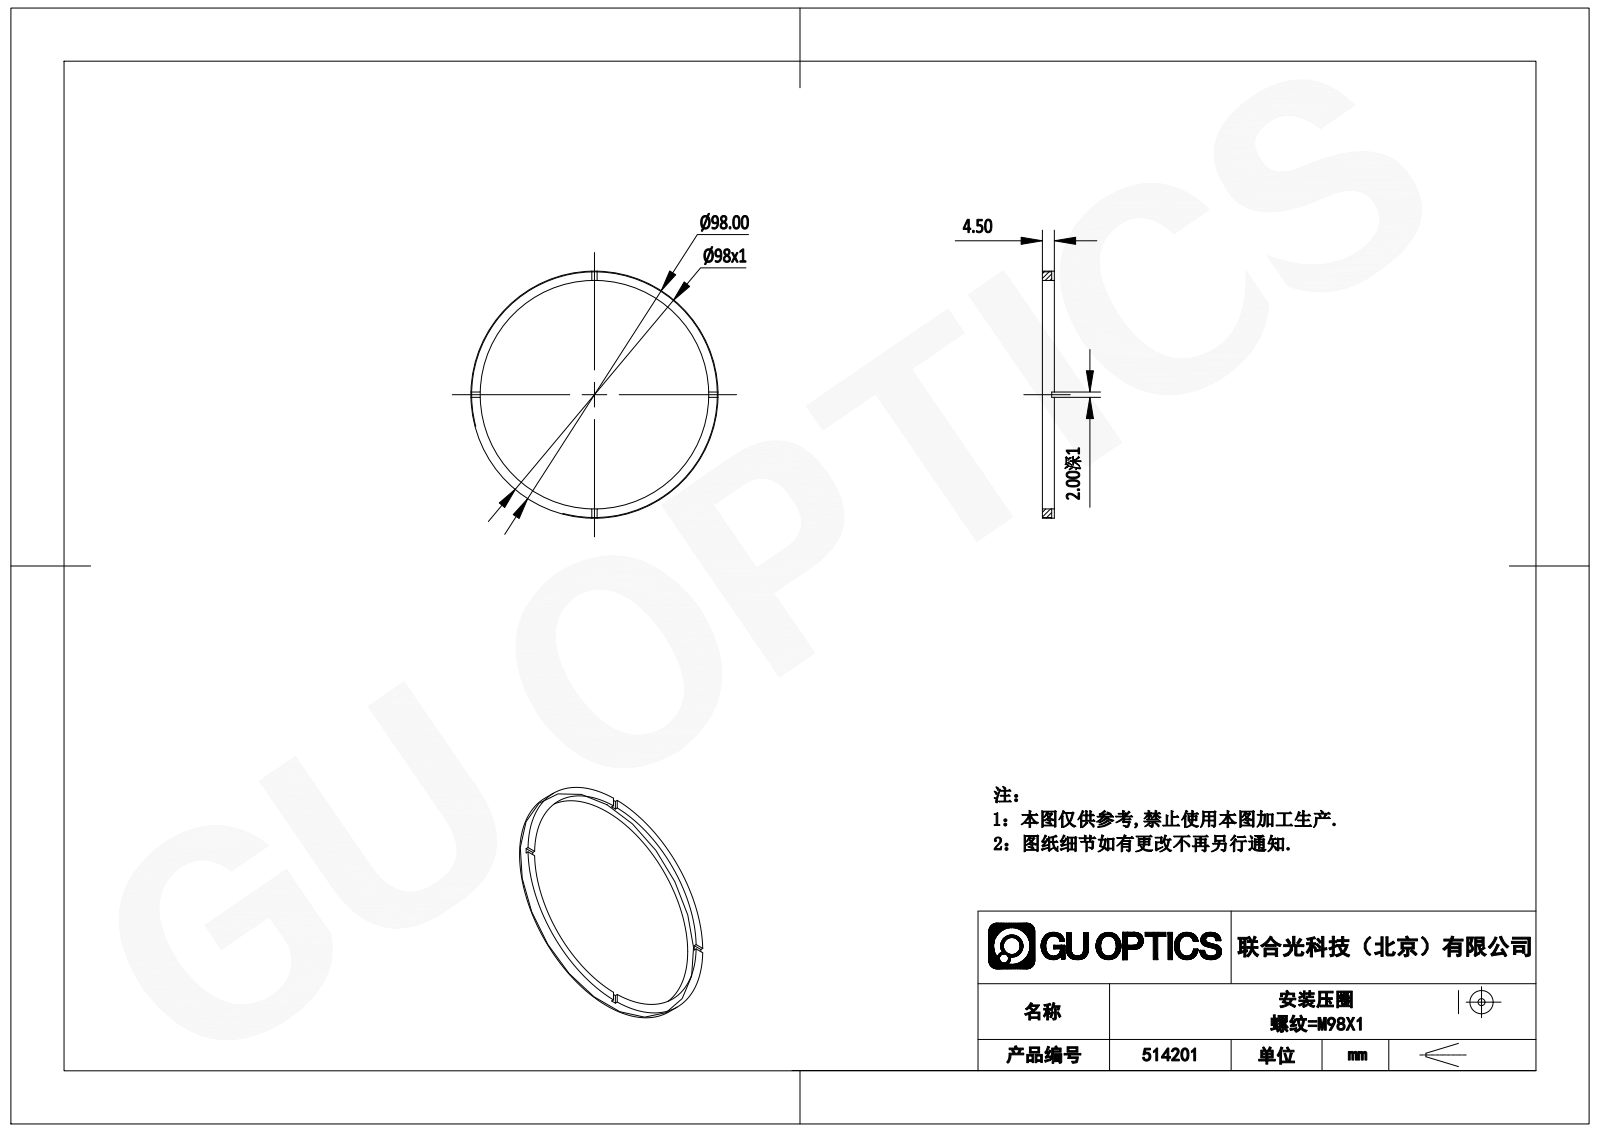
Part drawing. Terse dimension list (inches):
name: 514201
written by: SolidWorks 2020 (CONFIG_CONTROL_DESIGN)
unit: in
bodies: 1 solid, 21 faces (17 planar, 4 cylindrical, 0 other)
size: 3.858 × 3.858 × 0.177
volume: 0.284 in³; area: 7.381 in²
holes: 1× ⌀3.583
bosses: 1× ⌀3.858
face distances: 0.177, 0.138, 0.039, 0.079
